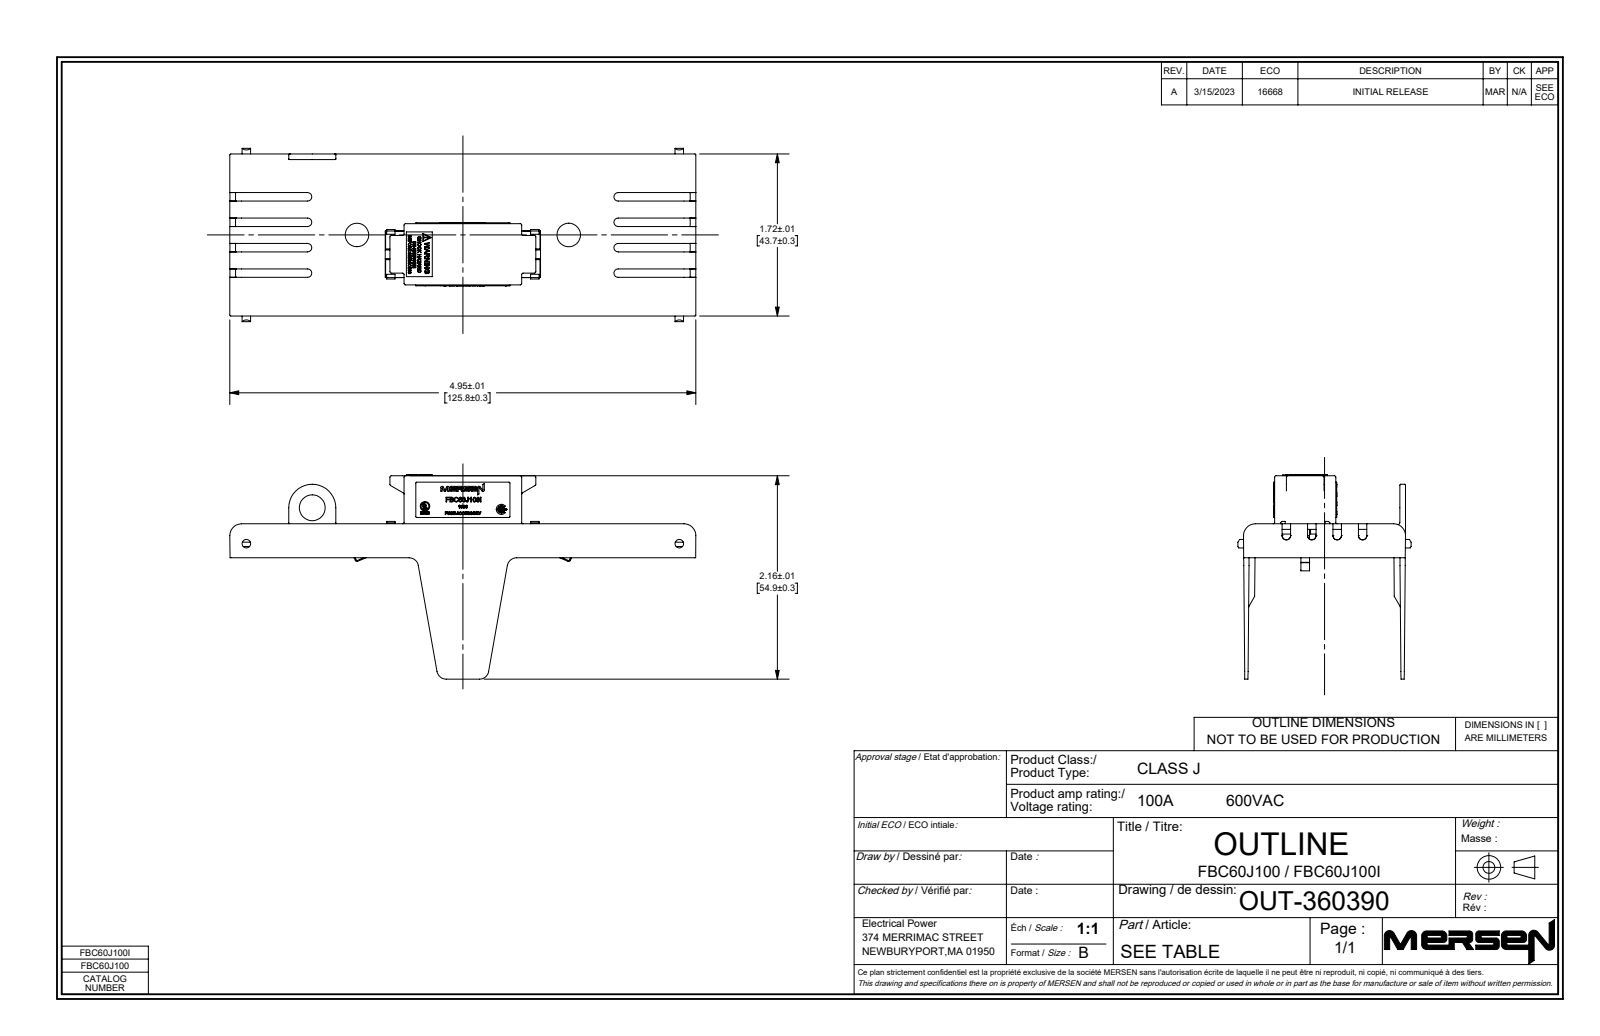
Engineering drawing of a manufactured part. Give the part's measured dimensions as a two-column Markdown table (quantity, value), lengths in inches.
| quantity | value |
| --- | --- |
| part name | OUT-360390; 1203190; 1203188_FBC60J30I; 1203656 (+1 more) |
| STEP written by | SolidWorks 2021 (AUTOMOTIVE_DESIGN) |
| units | inches |
| bodies | 4 solids, 2341 faces (1234 planar, 206 cylindrical, 901 other) |
| overall size | 4.951 × 2.171 × 1.84 |
| volume | 0.929 in³ |
| surface area | 34.21 in² |
| round holes (diameter × count) | 0.25 × 2, 0.275 × 1 |
| round bosses / shafts (diameter × count) | 0.09 × 2 |
| partial cylindrical surfaces (radius × count) | 0.01 × 67, 0.015 × 32, 0.045 × 16, 0.065 × 4, 0.1 × 4, 0.125 × 4, 0.15 × 2, 0.02 × 1 |
| main face-to-face distances | 0.06, 1.66, 0.078, 0.572, 0.57, 0.51, 0.65, 4.89, 0.361, 0.301 |
| hole center spacings | 2.25 |
